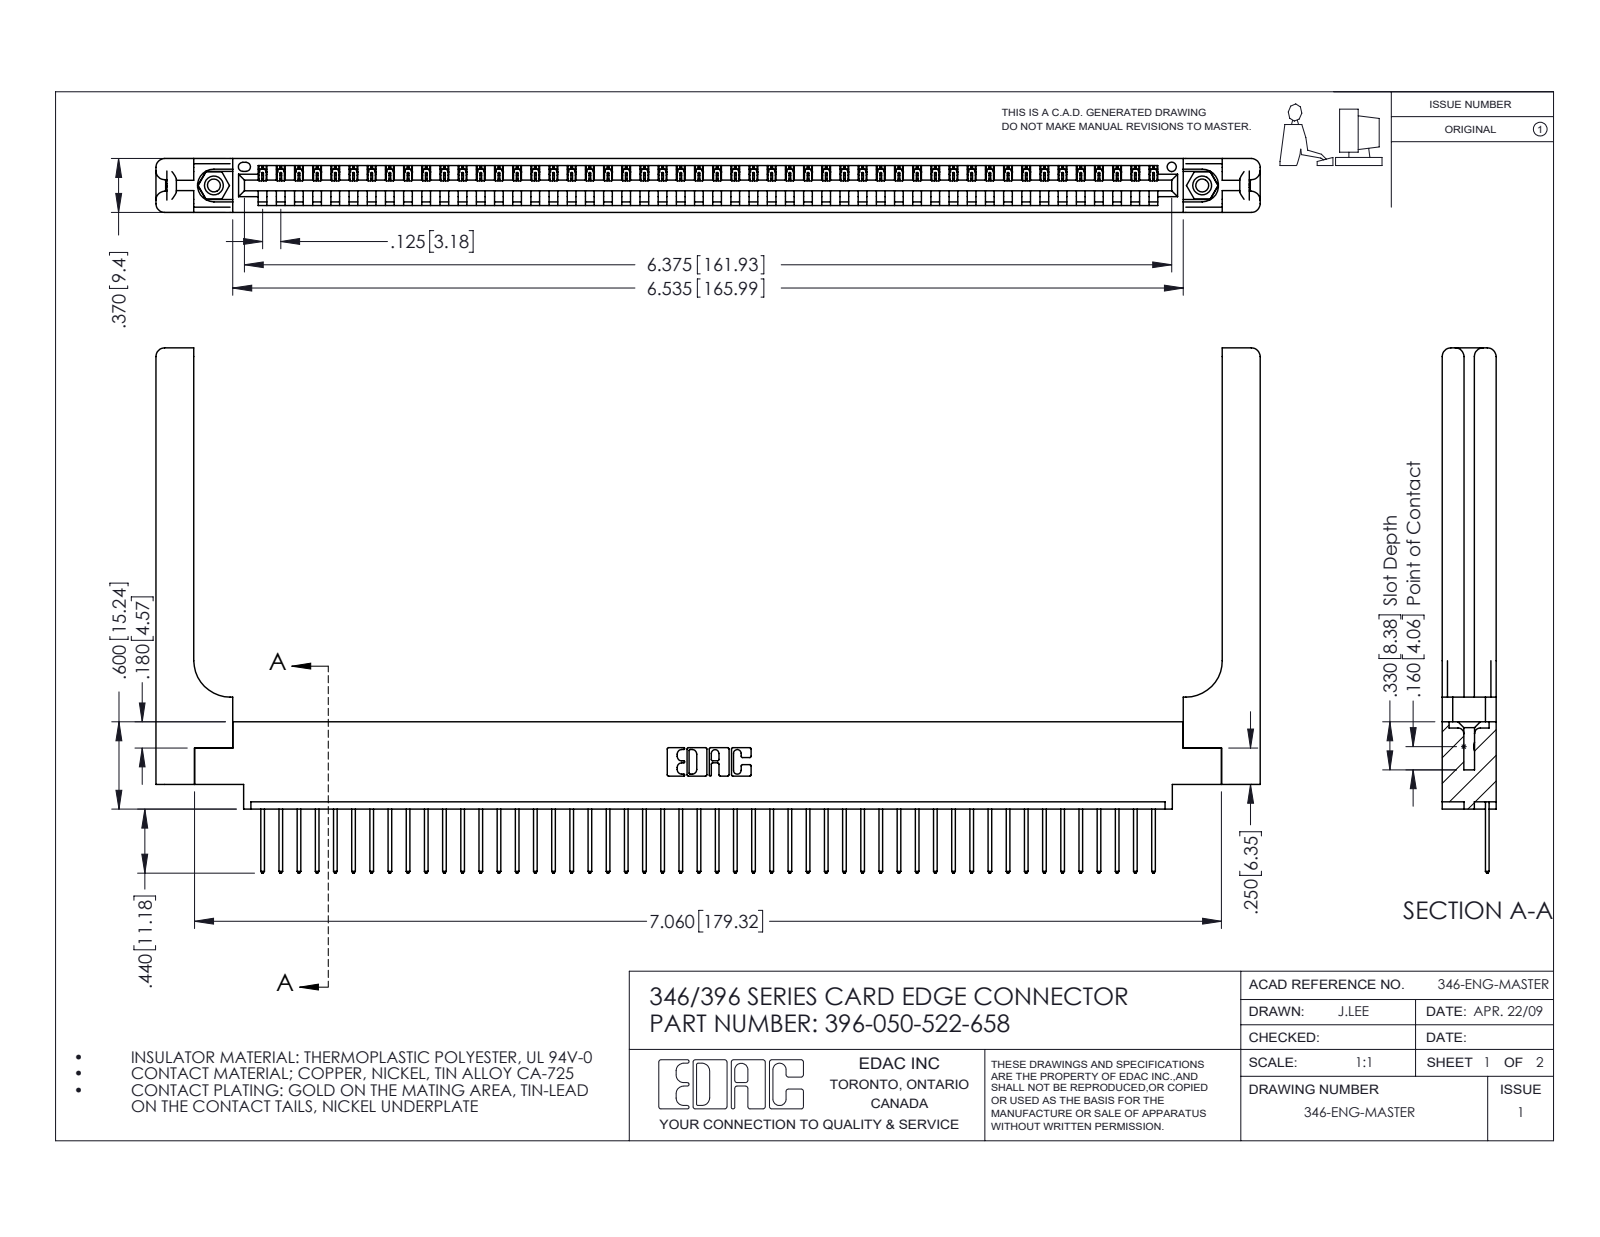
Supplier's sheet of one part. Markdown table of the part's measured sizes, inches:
| quantity | value |
| --- | --- |
| part name | 396-050-522-658; 345-292-001_345-293-122; 346-220-058_345-220-058; 345-250-001_345-250-001-102 (+1 more) |
| STEP written by | SolidWorks 2016 (CONFIG_CONTROL_DESIGN) |
| units | inches |
| bodies | 55 solids, 3282 faces (2228 planar, 994 cylindrical, 60 other) |
| overall size | 7.591 × 3.61 × 0.37 |
| volume | 1.579 in³ |
| surface area | 44.26 in² |
| round holes (diameter × count) | 0.089 × 2, 0.125 × 2, 0.156 × 2, 0.064 × 1 |
| round bosses / shafts (diameter × count) | 0.155 × 2 |
| partial cylindrical surfaces (radius × count) | 0.006 × 100, 0.01 × 100, 0.01 × 22, 0.06 × 16, 0.007 × 6, 0.031 × 6, 0.026 × 3, 0.03 × 2 |
| main face-to-face distances | 0.37, 0.048, 0.322, 0.072, 0.148, 0.15, 0.25, 0.298, 0.025, 0.222 |
| hole center spacings | 0.246, 6.586, 6.795 |
